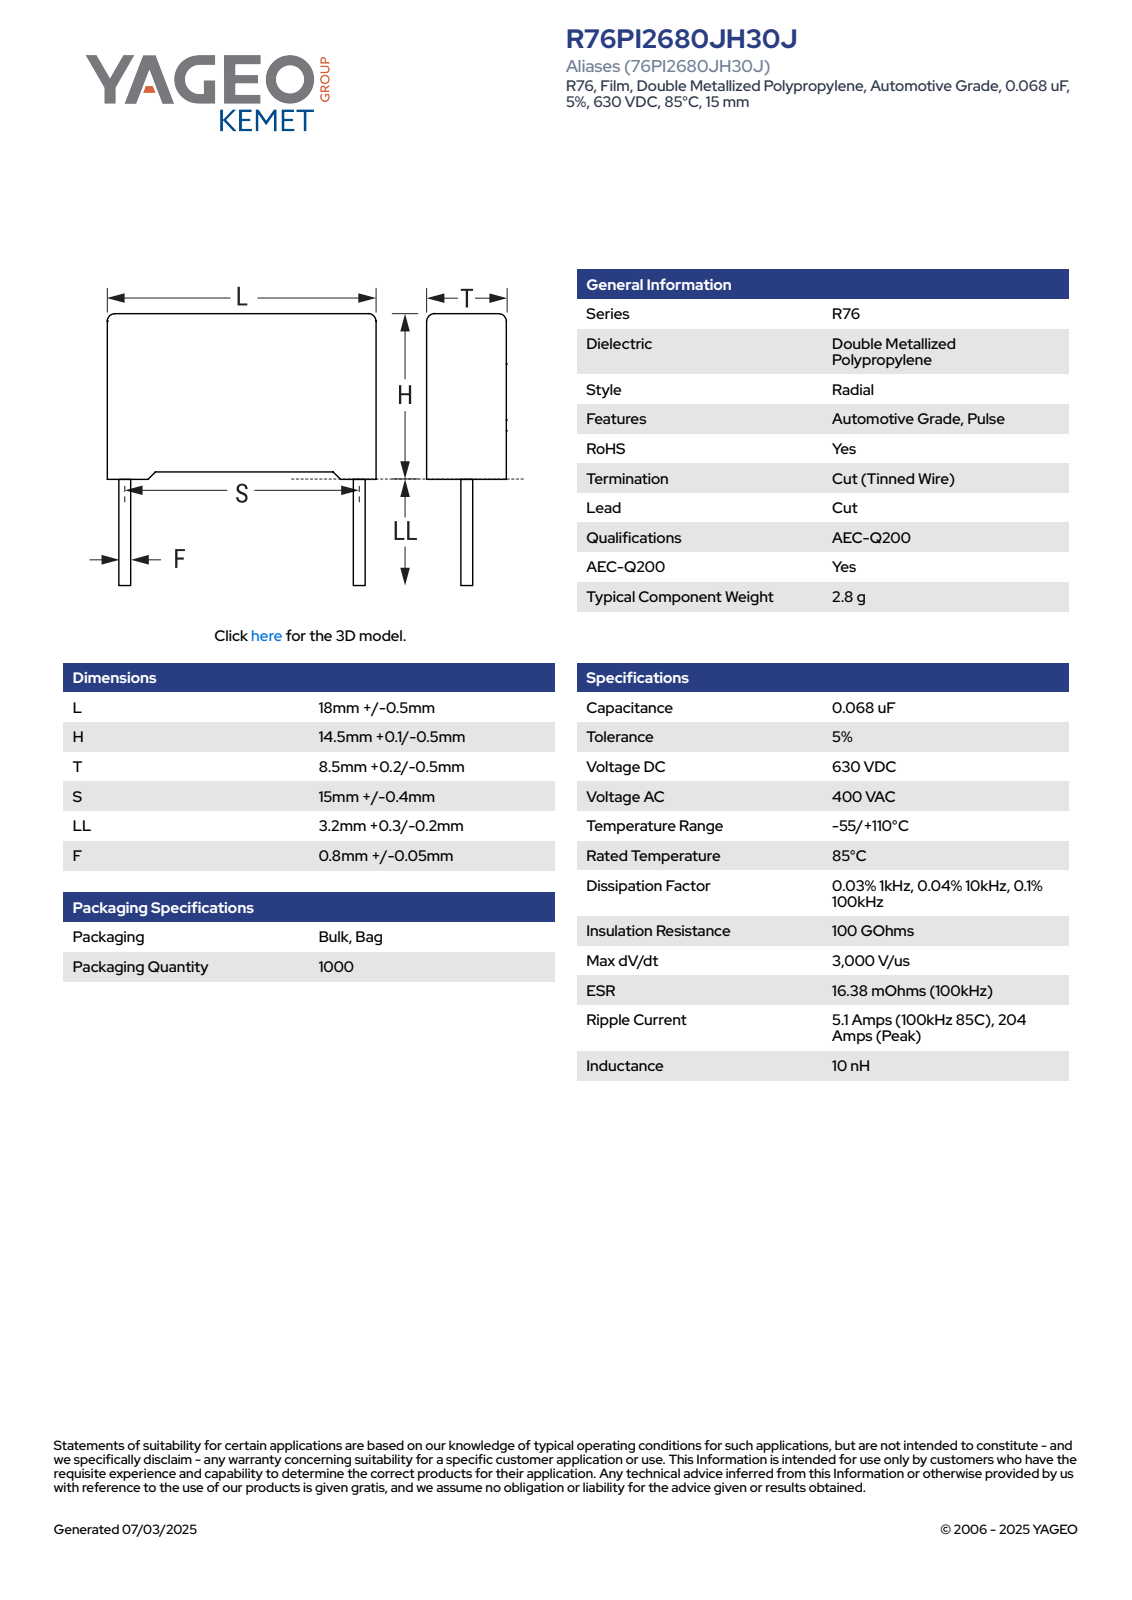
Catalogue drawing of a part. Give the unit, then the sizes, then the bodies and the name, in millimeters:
Units: millimetres
Overall size (bounding box): 18.5 × 18.1 × 8.71
Round bosses / shafts (diameter × count): ⌀0.85 ×2
Partial cylindrical surfaces — rounded edges, fillets, slot ends (radius × count): R0.5 ×4
Main face-to-face distances: 8.7, 13.85, 18.5, 0.62, 0.75, 14.6, 8.08, 0.5, 14.1, 17.88
Volume: 2 248 mm³ · Surface area: 1 167 mm²
Bodies: 4 solids, 85 faces (77 planar, 8 cylindrical, 0 other)
Part name (STEP PRODUCT): CFR_RB2_18X14.5X8.5_L18.5H14.6T8.7S15LL3.5F0.85
STEP written by: SolidWorks 2021 (AUTOMOTIVE_DESIGN)
